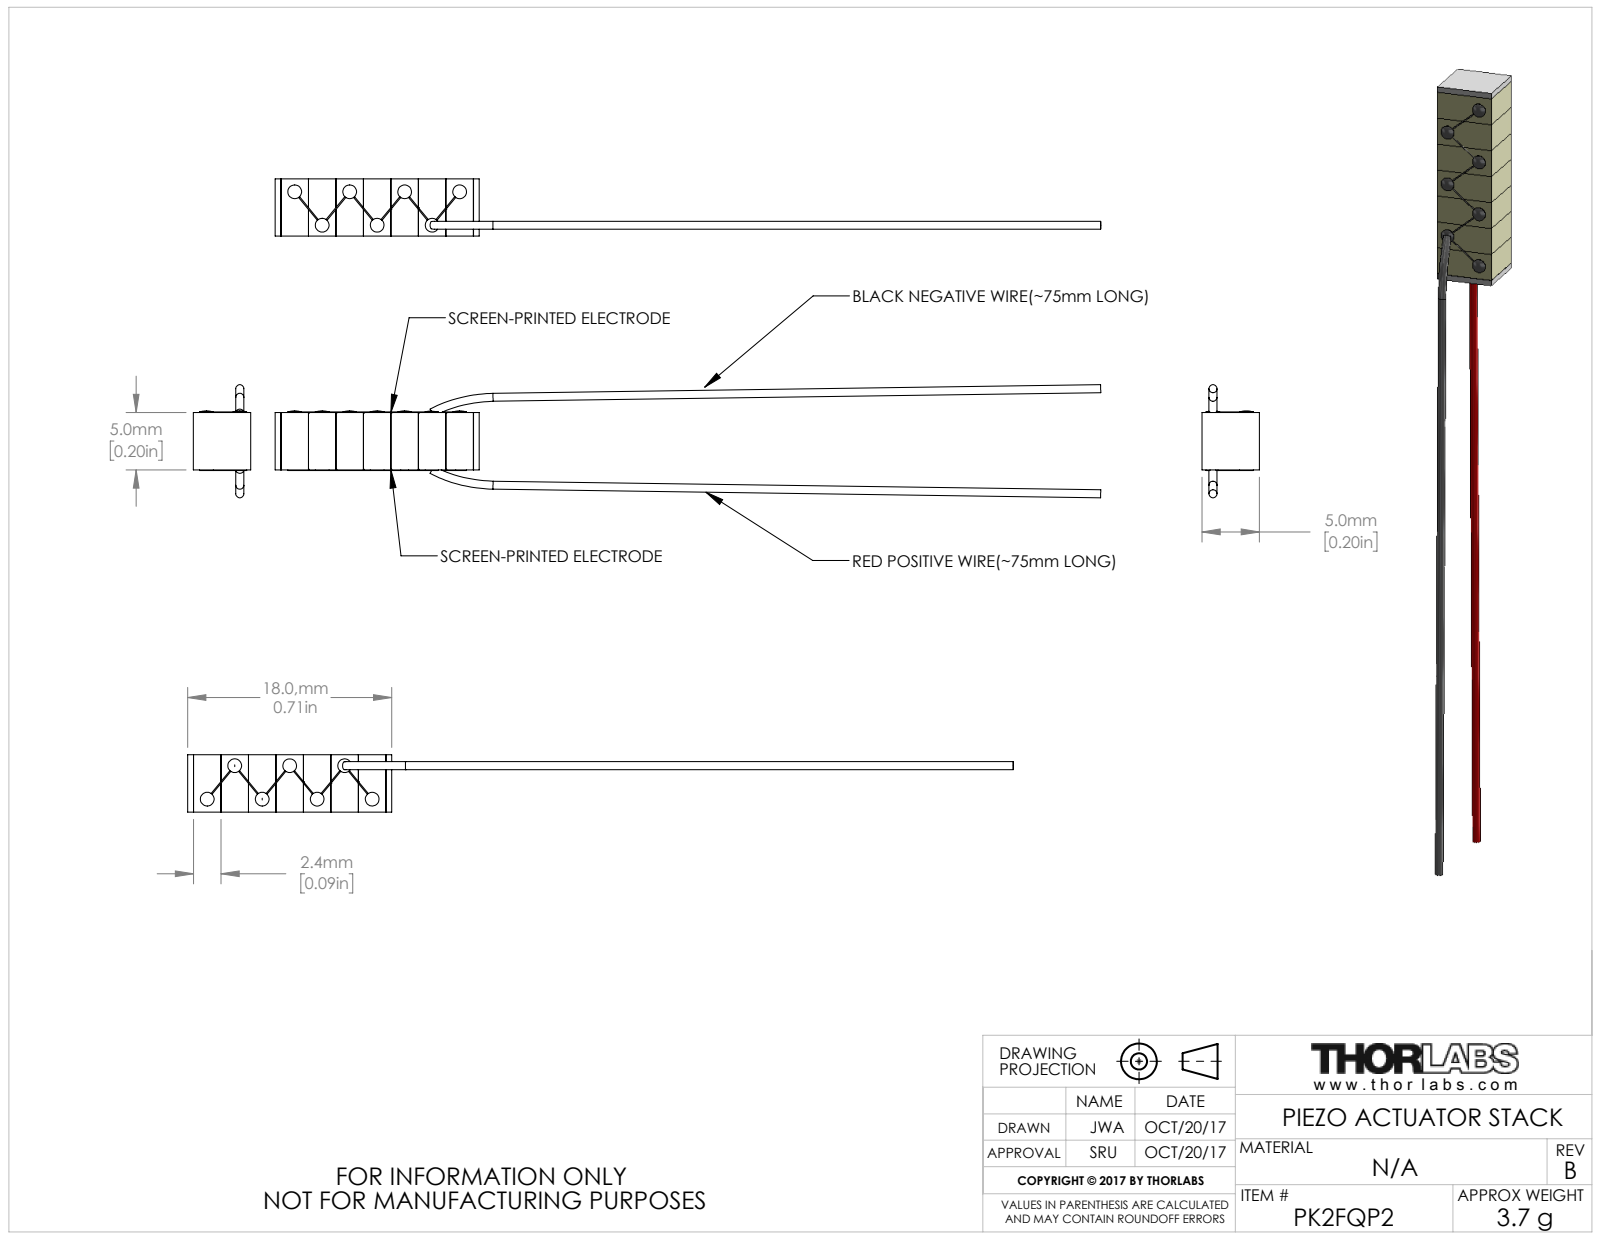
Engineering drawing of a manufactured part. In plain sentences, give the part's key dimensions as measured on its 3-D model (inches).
The part is named "CTN002573". Its 3-D file was written by "SolidWorks 2016 (AUTOMOTIVE_DESIGN)". It is 9 solids with 161 faces: 76 planar, 66 cylindrical and 19 other. Overall it measures 2.838 by 0.389 by 0.197 inches. Its volume is 0.03 cubic inches and its surface area 1.672 square inches. Round bosses or shafts: 7 of diameter 0.047, 2 of diameter 0.028. The main face-to-face distances are 0.094, 0.189, 0.283, 0.378, 0.197, 0.472, 0.567, 0.02, 0.681, 0.587.
